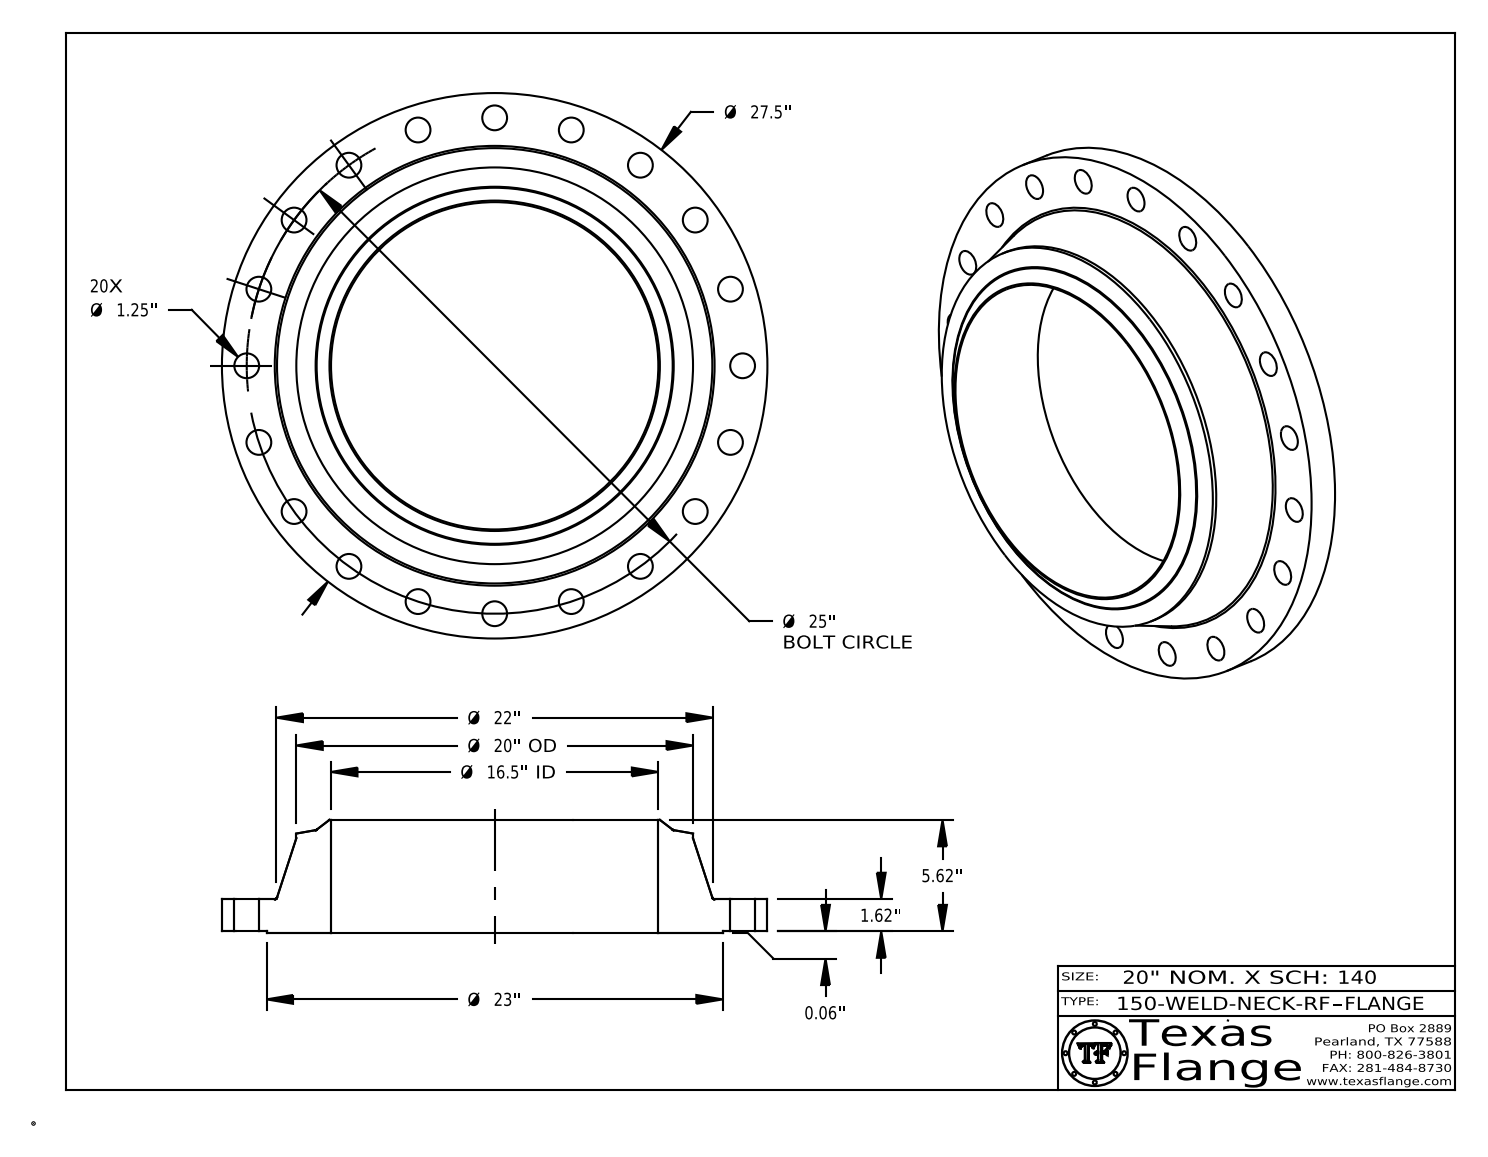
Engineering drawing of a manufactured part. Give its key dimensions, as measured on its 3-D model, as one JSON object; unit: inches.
{"part_name": "150-WELD-NECK-RF", "step_written_by": "CATIA V5 STEP AP214 (AUTOMOTIVE_DESIGN)", "units": "inches", "bodies": {"solids": 1, "faces": 447, "planar": 369, "cylindrical": 68, "other": 10}, "overall_size": [27.5, 27.5, 5.683], "volume_in3": 1044, "surface_area_in2": 1448, "round_holes": [[1.25, 20], [0.495, 1], [16.5, 1]], "round_bosses_or_shafts": [[0.03, 8], [27.5, 1], [23, 1], [20, 1], [0.39, 1]], "face_to_face_distances": [1.683, 0.063, 1.62, 5.683, 5.62, 4, 1.668, 1.605, 0.015, 4.015], "hole_center_spacings": [12.5, 14.694, 17.678, 20.225, 23.776, 24.692, 11.35, 22.275]}
